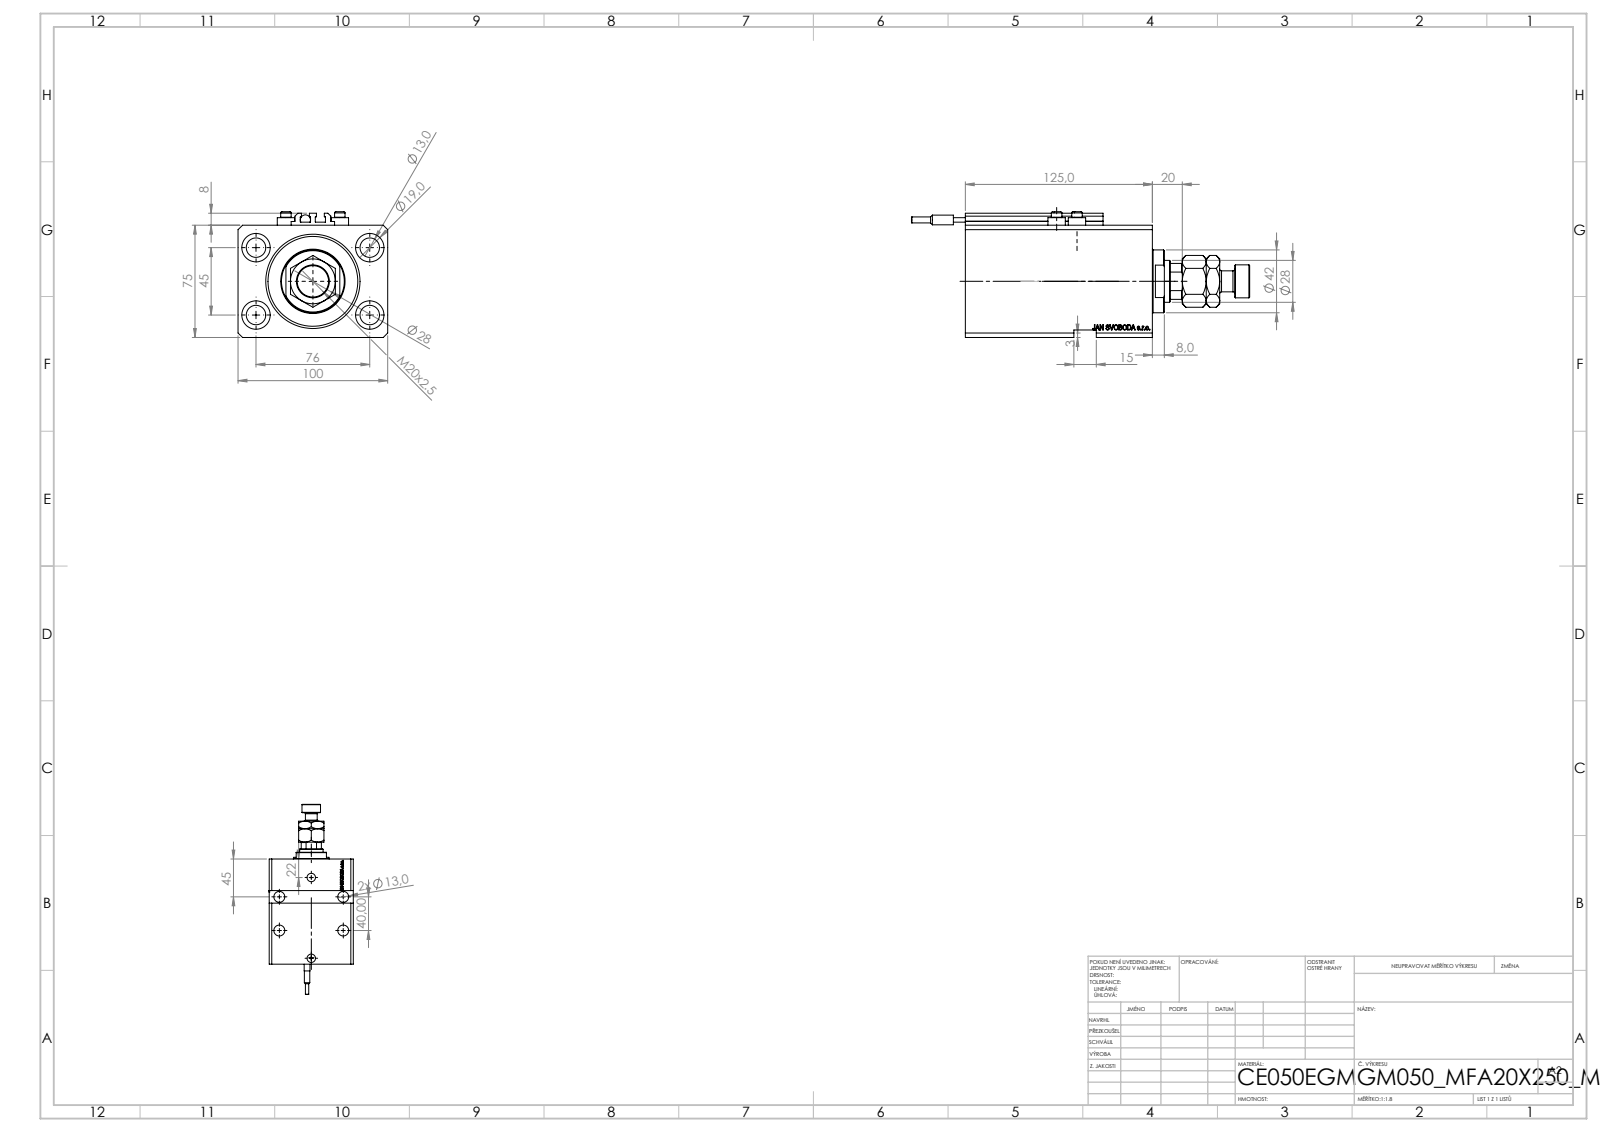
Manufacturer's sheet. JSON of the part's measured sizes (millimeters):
{"part_name": "V250CE_VC_E; MFA; SWITCH_V250CE; ALLEN BOLT V250CE (+2 more)", "step_written_by": "SolidWorks 2019 (CONFIG_CONTROL_DESIGN)", "units": "millimeters", "bodies": {"solids": 10, "faces": 1186, "planar": 567, "cylindrical": 156, "other": 463}, "overall_size": [226, 100, 84], "volume_mm3": 795233, "surface_area_mm2": 157314, "round_holes": [[13, 8], [1.25, 4], [4, 4], [19, 4], [10, 2], [13.16, 2], [20, 2], [18.5, 1], [28, 1], [50, 1], [63, 1]], "round_bosses_or_shafts": [[11.6, 4], [7, 4], [42, 1], [22, 1], [14, 1], [6.8, 1], [6.5, 1], [4, 1]], "partial_cylinders_radius": [[0.2, 10], [13.5, 1]], "face_to_face_distances": [75, 100, 20, 125, 11.9, 113.1, 105, 93.1, 70, 3], "hole_center_spacings": [44.16, 76, 13.6, 20.72, 27.59, 29, 33.62, 36]}
